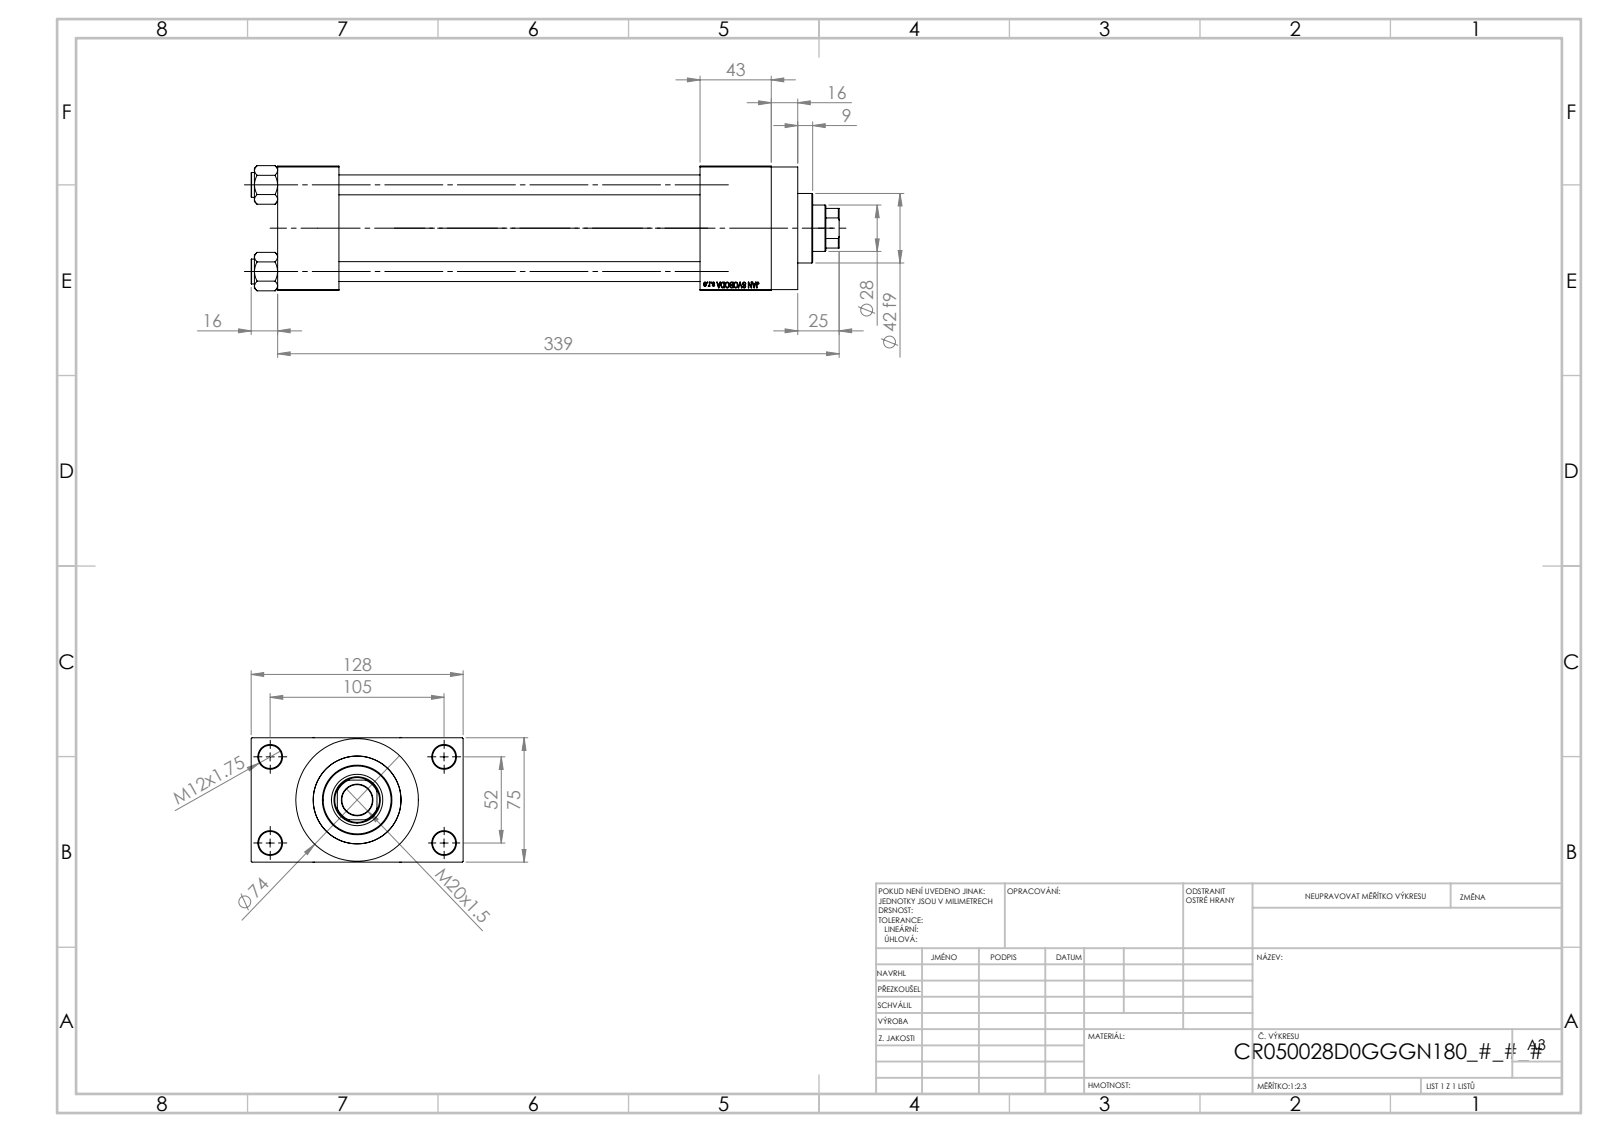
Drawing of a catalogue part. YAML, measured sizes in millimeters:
part_name: "V215CR_D_TYCINKA; NUT_M5_D; V215_VC_A; V215CR_VCP_D (+1 more)"
step_written_by: "SolidWorks 2019 (CONFIG_CONTROL_DESIGN)"
units: millimeters
bodies: {solids: 11, faces: 1104, planar: 497, cylindrical: 89, other: 518}
overall_size: [355, 128, 75.54]
volume: 1066000
surface_area: 260352
round_holes:
  - {diameter: 12, count: 4}
  - {diameter: 14, count: 4}
  - {diameter: 7, count: 2}
  - {diameter: 20.96, count: 2}
  - {diameter: 30, count: 2}
  - {diameter: 18.5, count: 1}
  - {diameter: 28, count: 1}
  - {diameter: 31, count: 1}
  - {diameter: 41, count: 1}
  - {diameter: 50, count: 1}
  - {diameter: 53, count: 1}
round_bosses_or_shafts:
  - {diameter: 15, count: 4}
  - {diameter: 74, count: 1}
  - {diameter: 56, count: 1}
  - {diameter: 42, count: 1}
partial_cylinders:
  - {radius: 13.5, count: 1}
face_to_face_distances: [75, 218, 37, 255, 26.5, 101.5, 298, 261, 43, 16]
hole_center_spacings: [26.35, 36.98, 52.3, 58.43, 58.59, 78.65, 94.37, 52]
